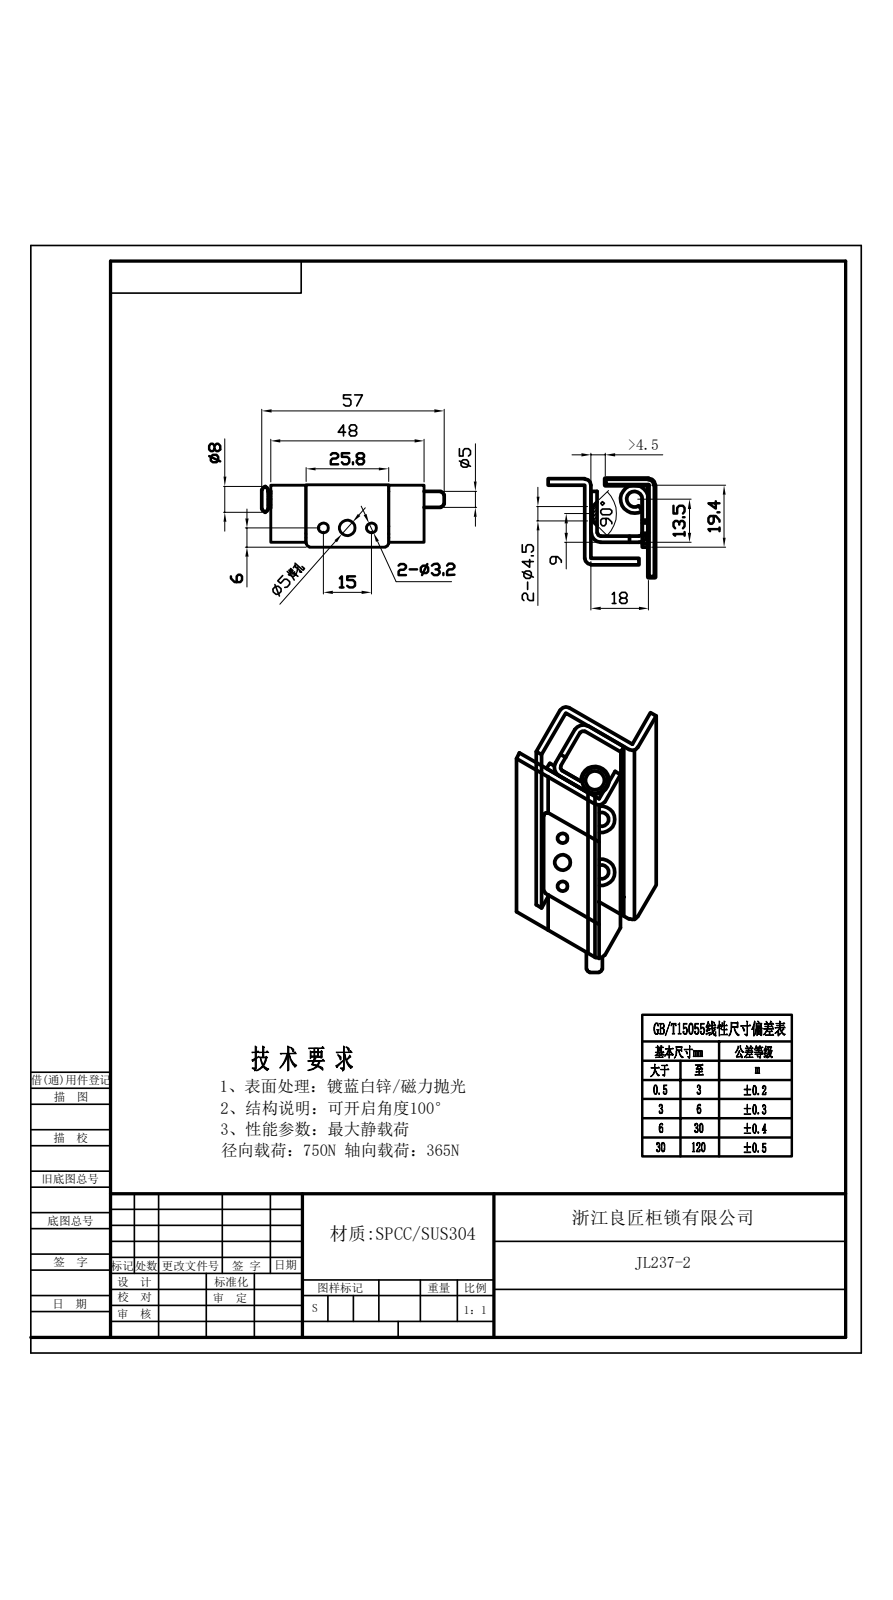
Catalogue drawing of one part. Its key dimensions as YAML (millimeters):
step_written_by: "Rhino 8.5 (CONFIG_CONTROL_DESIGN)"
units: millimeters
bodies: {solids: 3, faces: 228, planar: 28, cylindrical: 190, other: 10}
overall_size: [57, 19.4, 18]
volume: 6394
surface_area: 7396
round_holes:
  - {diameter: 3.2, count: 2}
  - {diameter: 4.5, count: 2}
  - {diameter: 5, count: 1}
round_bosses_or_shafts:
  - {diameter: 8.8, count: 1}
  - {diameter: 5, count: 1}
partial_cylinders:
  - {radius: 1, count: 4}
  - {radius: 1.1, count: 2}
  - {radius: 3, count: 2}
  - {radius: 2.62, count: 1}
face_to_face_distances: [1.9, 16.1, 18, 14.2, 11, 37, 11.1, 36.9, 25.9, 48]
hole_center_spacings: [7.03, 7.5, 13.66, 20.89, 15, 25.8]
